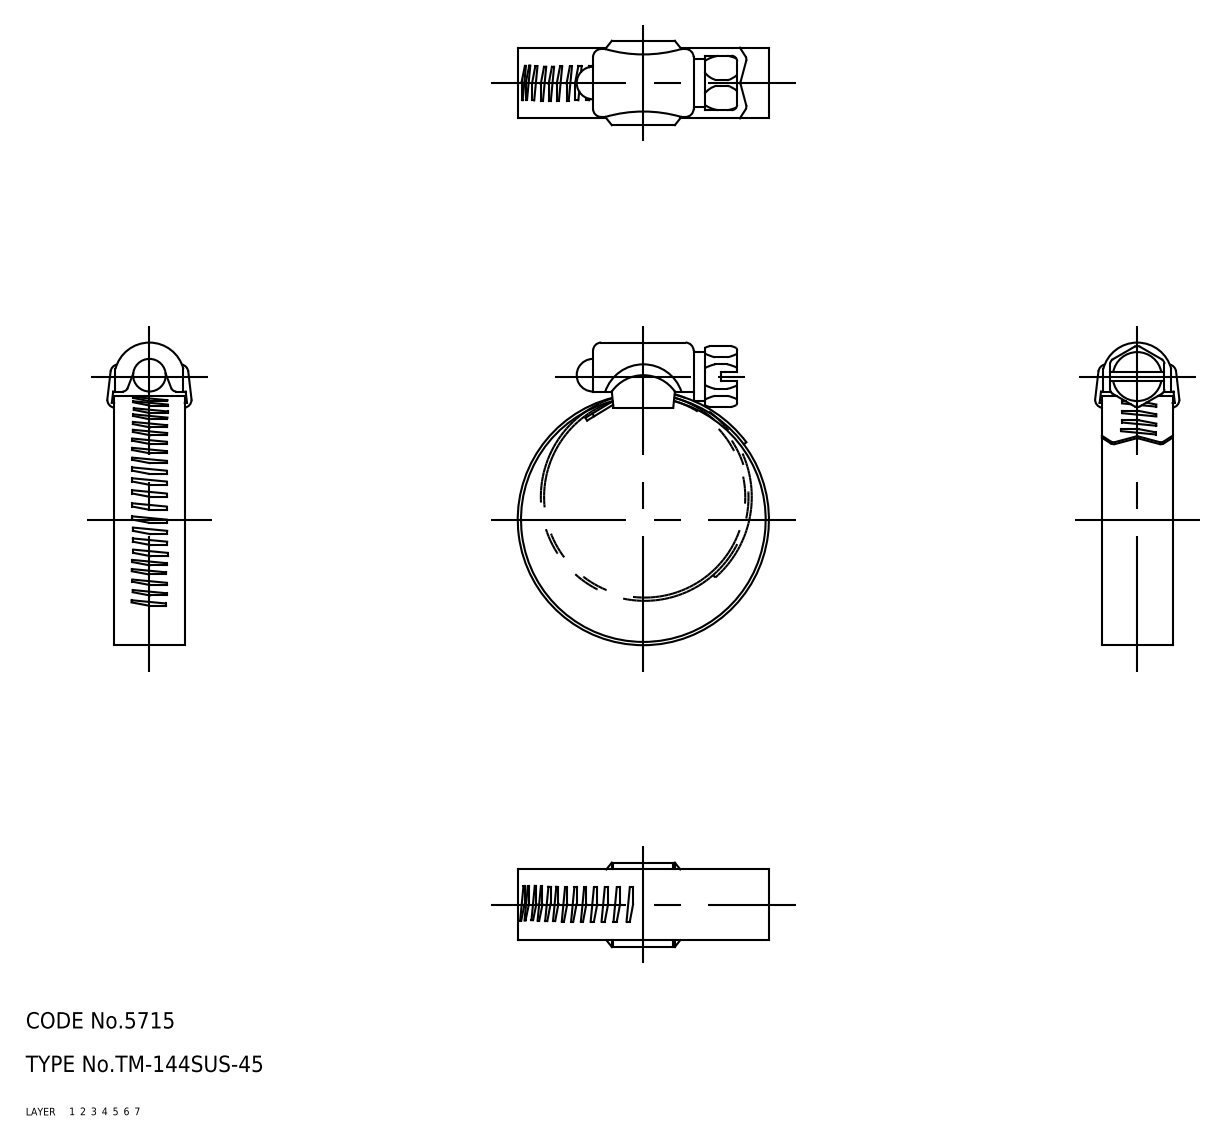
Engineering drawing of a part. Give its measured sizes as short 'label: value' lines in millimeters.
name: screw; holder; band; TM_144SUS_45_20697_36
written by: CADfix (AUTOMOTIVE_DESIGN)
unit: mm
bodies: 3 solids, 214 faces (0 planar, 0 cylindrical, 214 other)
size: 55.66 × 46.2 × 15.63
volume: 3 562 mm³; area: 6 967 mm²
